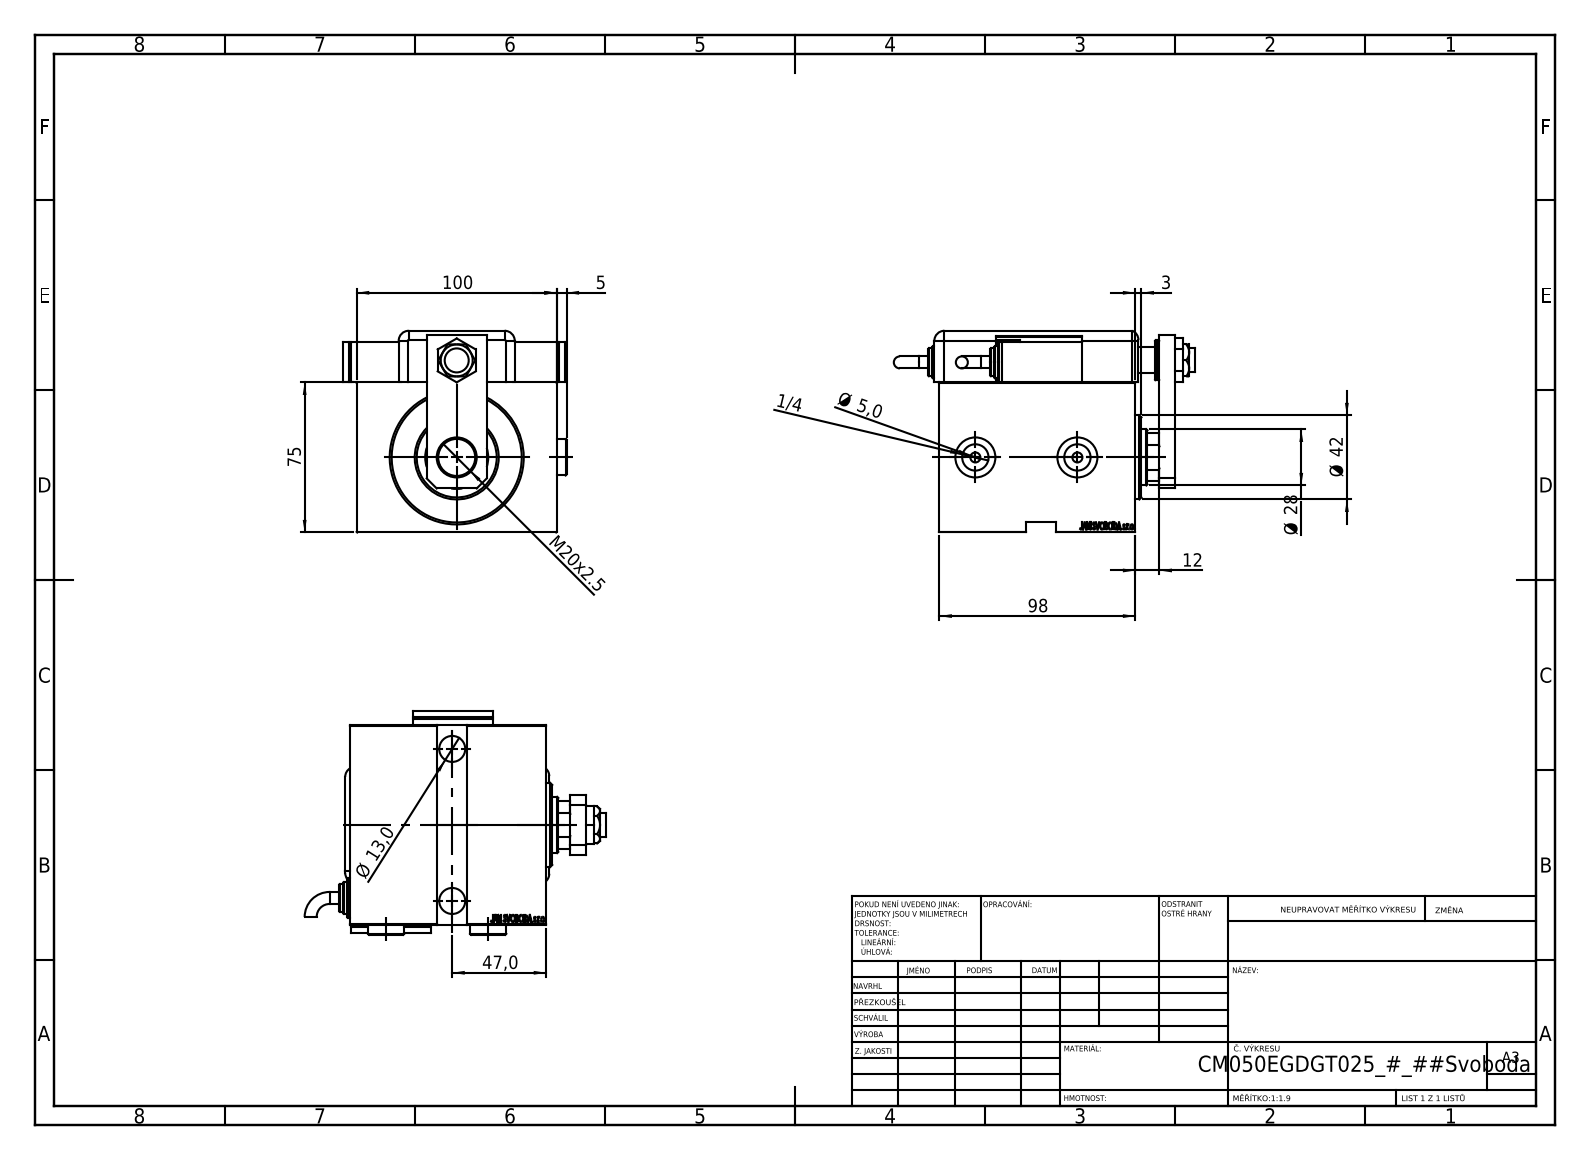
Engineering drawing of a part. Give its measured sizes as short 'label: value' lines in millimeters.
name: SWITCH DIM A_G; ZARAZKA_Q; MAGNETIC SWITCH Q; SWITCH Q (+7 more)
written by: SolidWorks 2019 (CONFIG_CONTROL_DESIGN)
unit: mm
bodies: 15 solids, 1286 faces (650 planar, 115 cylindrical, 521 other)
size: 150.46 × 111.9 × 100.8
volume: 804 121 mm³; area: 153 952 mm²
holes: 3× ⌀13, 3× ⌀20, 2× ⌀4, 2× ⌀5, 2× ⌀8, 2× ⌀13.16, 2× ⌀19, 1× ⌀12, 1× ⌀14, 1× ⌀18.5, 1× ⌀28, 1× ⌀31.5
bosses: 3× ⌀20, 2× ⌀18, 2× ⌀16, 2× ⌀14, 2× ⌀6, 1× ⌀52, 1× ⌀42
rounds: 9× R5, 1× R10, 1× R13.5
face distances: 3, 75, 98, 100, 5, 14, 20, 84, 79, 100.8
hole spacings: 47.2, 61.22, 20, 48.5, 51, 76
